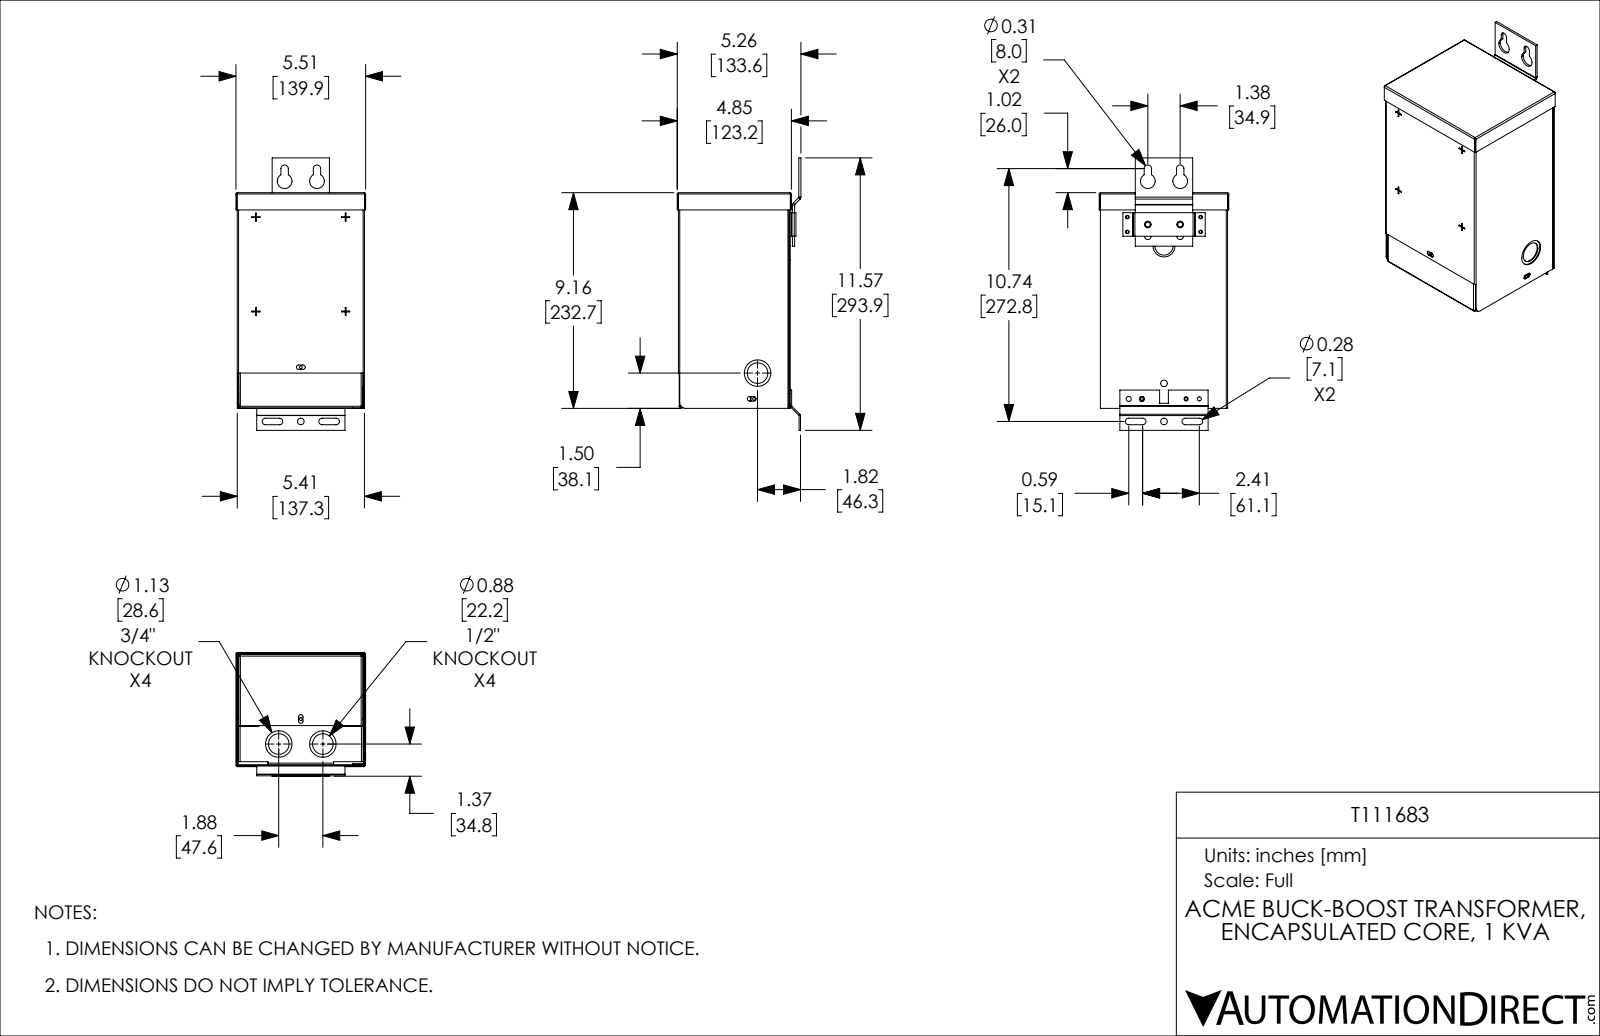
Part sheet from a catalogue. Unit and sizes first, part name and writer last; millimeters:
Units: millimetres
Overall size (bounding box): 293.87 × 139.9 × 133.57
Round holes (diameter × count): ⌀7.14 ×6, ⌀3.05 ×5, ⌀22.22 ×3, ⌀28.57 ×3, ⌀4.37 ×2, ⌀4.76 ×2, ⌀5.11 ×2, ⌀5.56 ×2, ⌀15.88 ×2
Round bosses / shafts (diameter × count): ⌀29.79 ×1, ⌀23.44 ×1
Partial cylindrical surfaces — rounded edges, fillets, slot ends (radius × count): R0.51 ×10, R2.38 ×10, R0.79 ×8, R1.42 ×8, R1.7 ×8, R0.38 ×4, R1.9 ×4, R3.57 ×4
Main face-to-face distances: 0.91, 119.74, 136.41, 118.83, 135.5, 137.32, 120.65, 231.14, 1.29, 2.2
Hole centre spacings: 34.92, 12.7, 14.29, 29.09, 34.08, 35.98, 37.16, 41.6
Volume: 177 414 mm³ · Surface area: 368 059 mm²
Bodies: 7 solids, 521 faces (329 planar, 152 cylindrical, 40 other)
Part name (STEP PRODUCT): T111683
STEP written by: SolidWorks 2021 (CONFIG_CONTROL_DESIGN)
